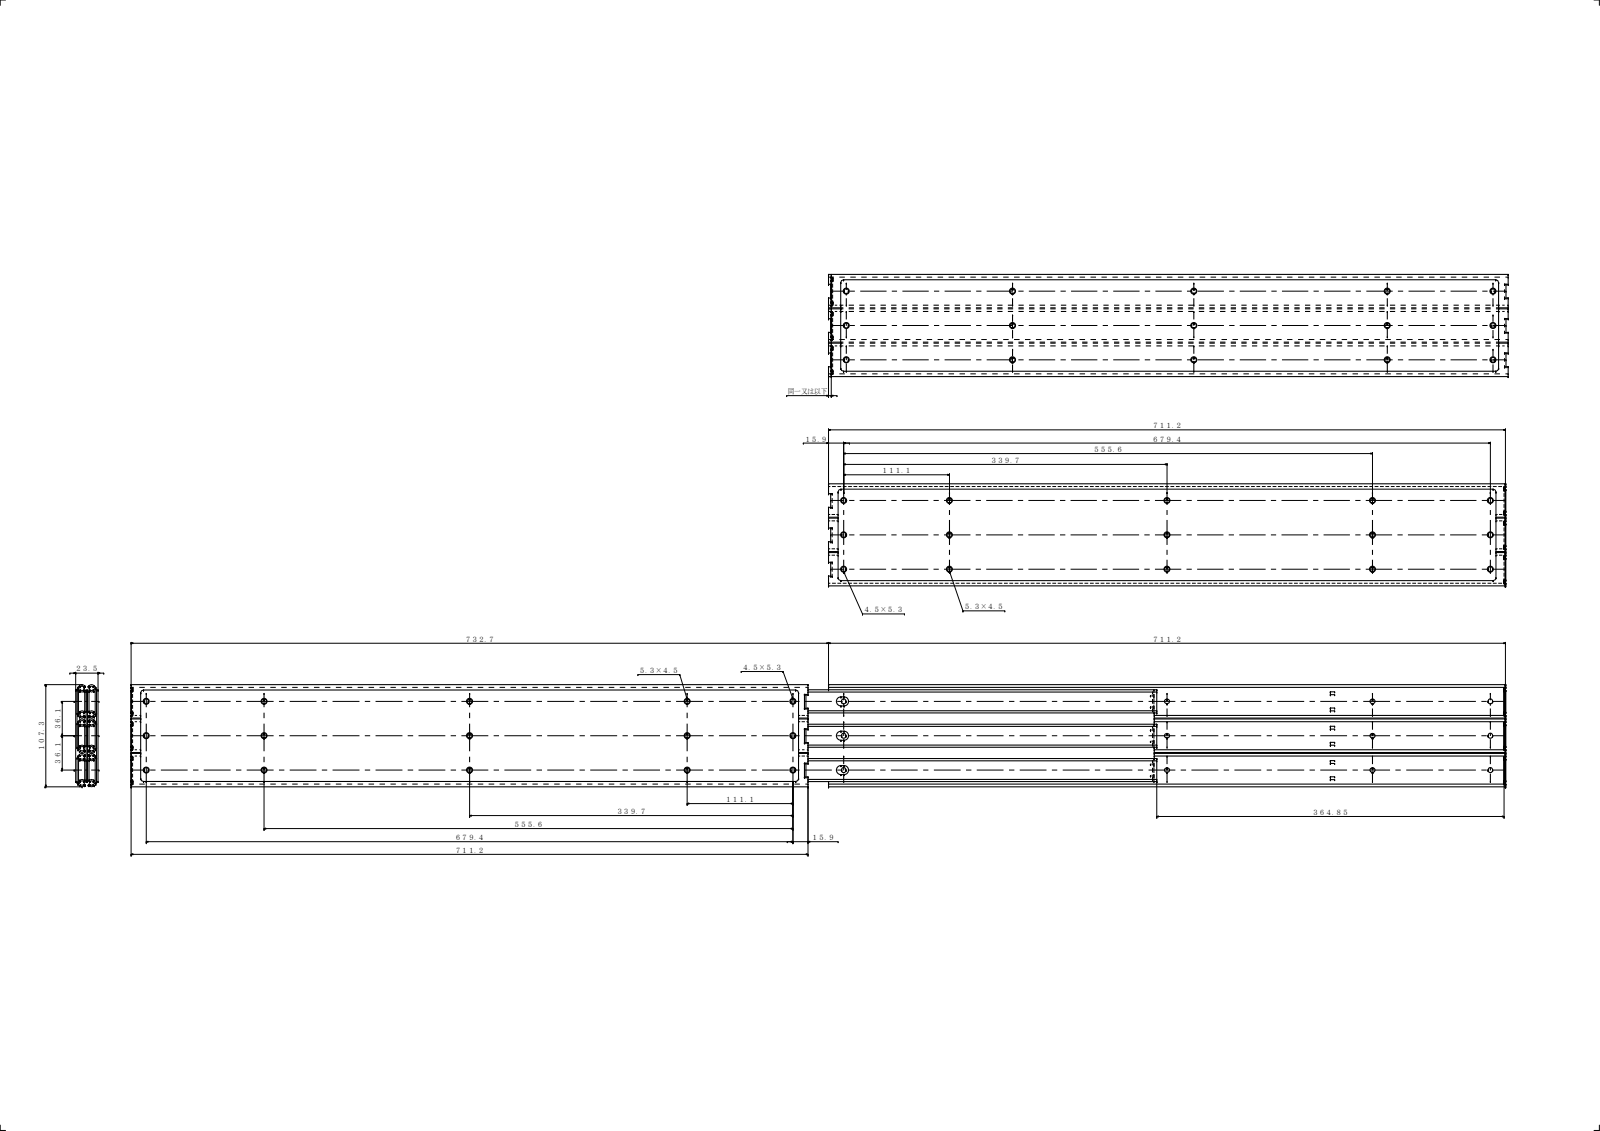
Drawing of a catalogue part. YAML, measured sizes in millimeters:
part_name: "IM U53-28; U53-28; IM継板-28; OM U53-28 (+1 more)"
step_written_by: "SolidWorks 2019 (CONFIG_CONTROL_DESIGN)"
units: millimeters
bodies: {solids: 15, faces: 963, planar: 456, cylindrical: 507, other: 0}
overall_size: [1443.9, 107.3, 23.5]
volume: 803492
surface_area: 1108000
round_holes:
  - {diameter: 6.4, count: 36}
  - {diameter: 6.5, count: 3}
partial_cylinders:
  - {radius: 2.25, count: 60}
  - {radius: 1, count: 48}
  - {radius: 0.4, count: 36}
  - {radius: 2, count: 36}
  - {radius: 3, count: 36}
  - {radius: 0.3, count: 12}
  - {radius: 1.3, count: 12}
  - {radius: 1.83, count: 12}
face_to_face_distances: [1.5, 11, 9.5, 20.5, 12.5, 3, 8, 22, 19, 14]
hole_center_spacings: [36.1, 72.2, 341.61, 339.7, 256.55, 347.29, 394.65, 480.06]
